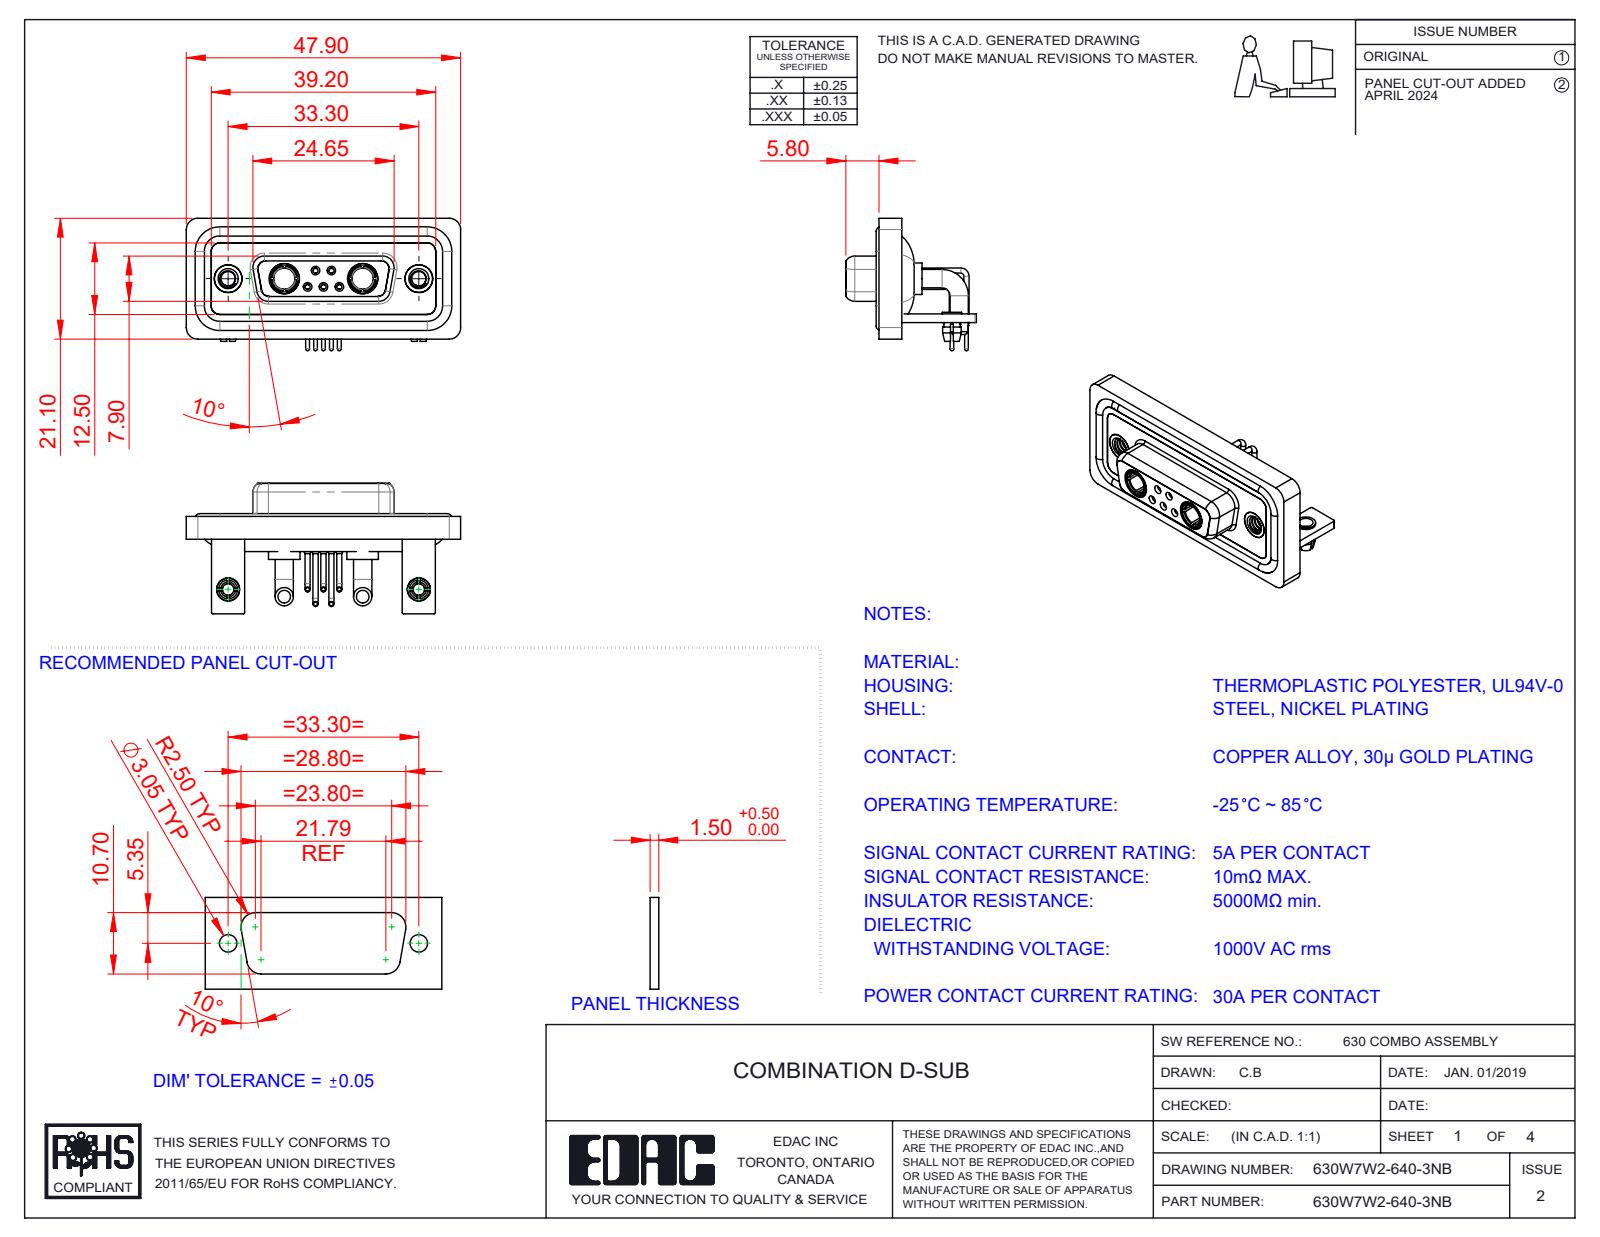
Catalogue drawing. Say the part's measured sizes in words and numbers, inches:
The part is named "630Combo Threaded Rivet_A; 630Combo Contact Row 2_50 Contacts; Power Socket_30A RA; 630Combo Board Lock_50 Contacts (+7 more)". Its 3-D file was written by "SolidWorks 2023 (CONFIG_CONTROL_DESIGN)". It is 20 solids with 941 faces: 306 planar, 407 cylindrical and 228 other. Overall it measures 1.886 by 0.91 by 0.898 inches. Its volume is 0.406 cubic inches and its surface area 17.35 square inches. Round holes: 7 of diameter 0.079, 5 of diameter 0.035, 5 of diameter 0.043, 5 of diameter 0.059, 4 of diameter 0.098, 4 of diameter 0.191, 3 of diameter 0.063, 2 of diameter 0.067, 2 of diameter 0.126, 2 of diameter 0.146, 2 of diameter 0.157, 2 of diameter 0.159. Round bosses or shafts: 6 of diameter 0.063, 5 of diameter 0.035, 5 of diameter 0.026, 4 of diameter 0.126, 2 of diameter 0.217, 2 of diameter 0.205, 2 of diameter 0.195, 2 of diameter 0.195. Partial cylindrical surfaces (rounded edges, fillets, slot ends): 21 of radius 0.079, 18 of radius 0.059, 16 of radius 0.01, 12 of radius 0.053, 8 of radius 0.063, 5 of radius 0.02, 4 of radius 0.024, 4 of radius 0.026. The main face-to-face distances are 0.016, 0.114, 0.059, 0.071, 0.146, 0.043, 0.161, 0.063, 0.098, 0.055. The hole center spacings are 0.124, 0.109, 0.386, 0.925, 1.311, 0.17, 0.17, 0.198.
